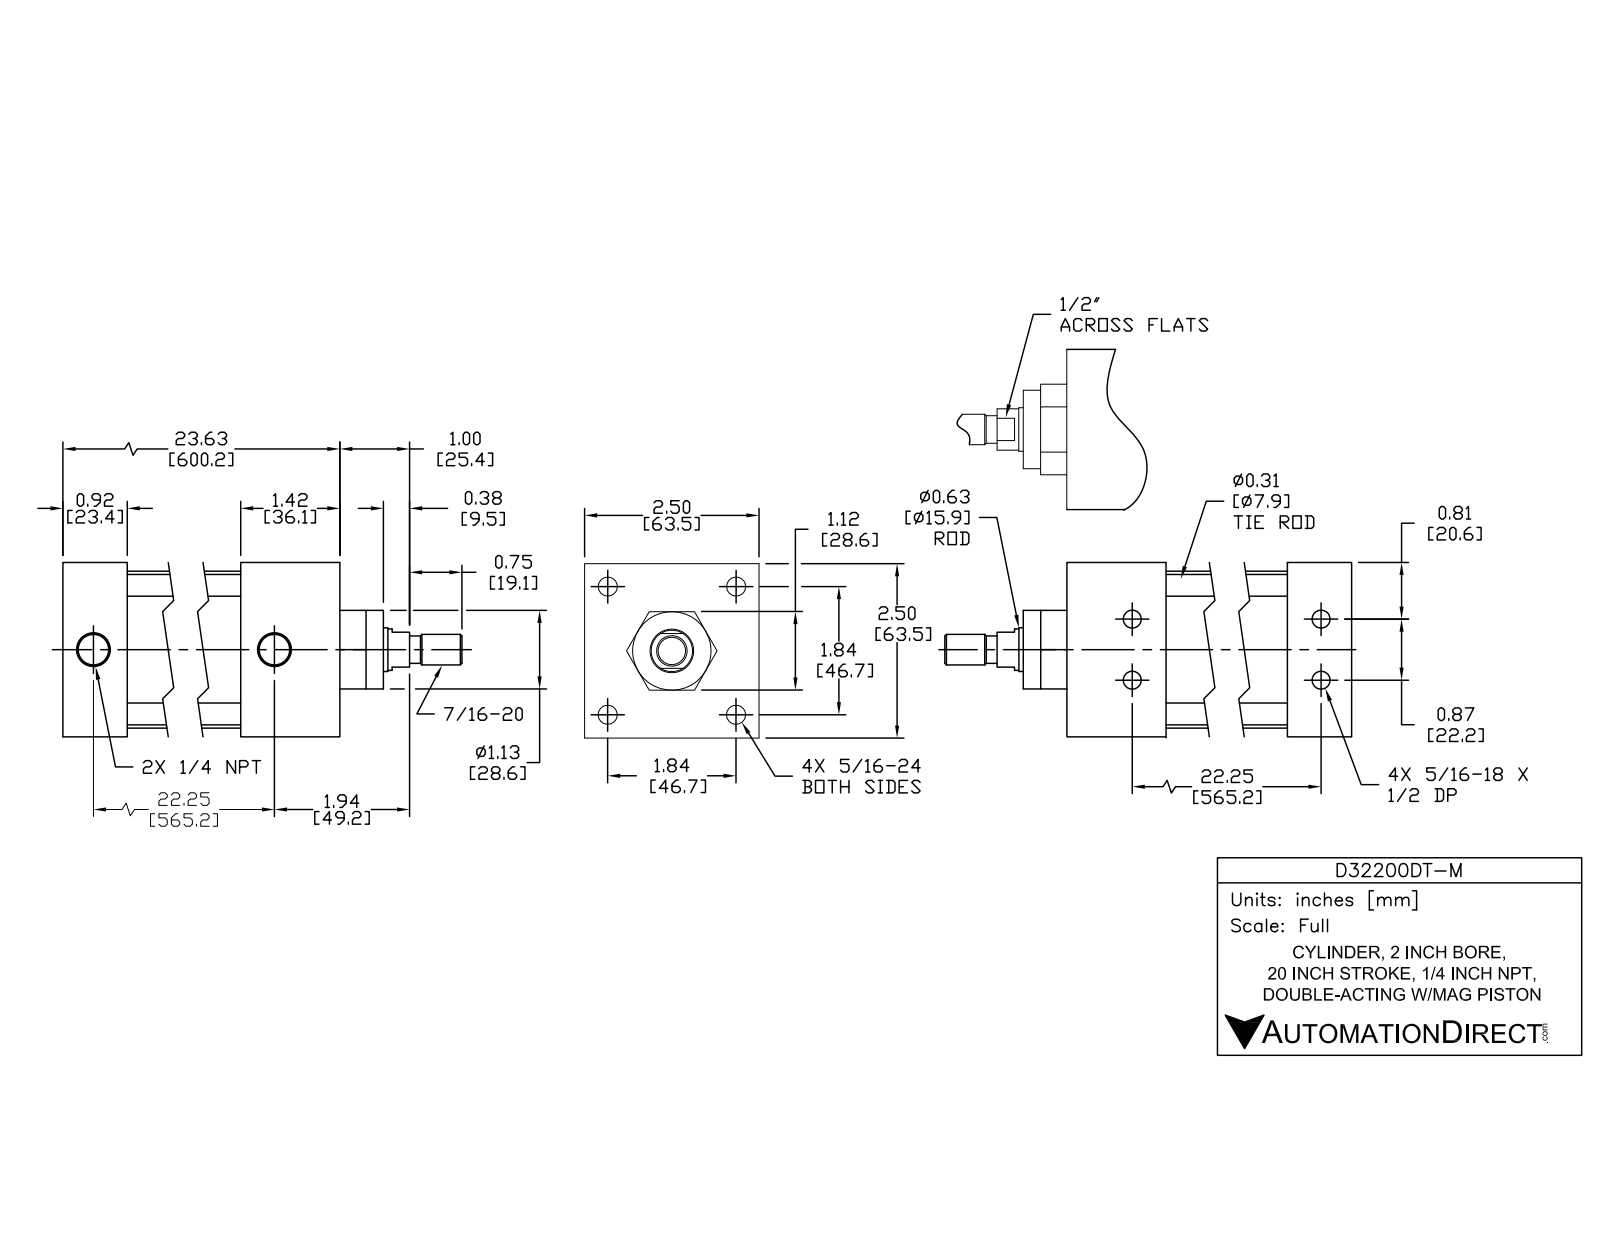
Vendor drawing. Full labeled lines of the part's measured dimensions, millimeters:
Part name (STEP PRODUCT): D32200DT-M; D32200DT-M BODY; D32200DT-M PISTON
STEP written by: SolidWorks 2015 (AUTOMOTIVE_DESIGN)
Units: millimetres
Bodies: 12 solids, 298 faces (94 planar, 114 cylindrical, 90 other)
Overall size (bounding box): 644.4 × 63.5 × 63.5
Volume: 780 000 mm³ · Surface area: 322 900 mm²
Round holes (diameter × count): ⌀6.4 ×4, ⌀6.8 ×4, ⌀9.1 ×4, ⌀12.7 ×4, ⌀7.5 ×2, ⌀12.1 ×2, ⌀15.9 ×1, ⌀16 ×1, ⌀50.8 ×1
Round bosses / shafts (diameter × count): ⌀12.3 ×4, ⌀8 ×4, ⌀7.2 ×4, ⌀57.2 ×1, ⌀50.7 ×1, ⌀28.4 ×1, ⌀15.8 ×1, ⌀15 ×1
Partial cylindrical surfaces — rounded edges, fillets, slot ends (radius × count): R6.4 ×4
Main face-to-face distances: 63.5, 2, 538.5, 600, 36.1, 563.9, 576.6, 540.5, 23.4, 25.4
Hole centre spacings: 33.2, 46.9, 565.2, 565, 11.1, 11.1, 22.2, 66.4
